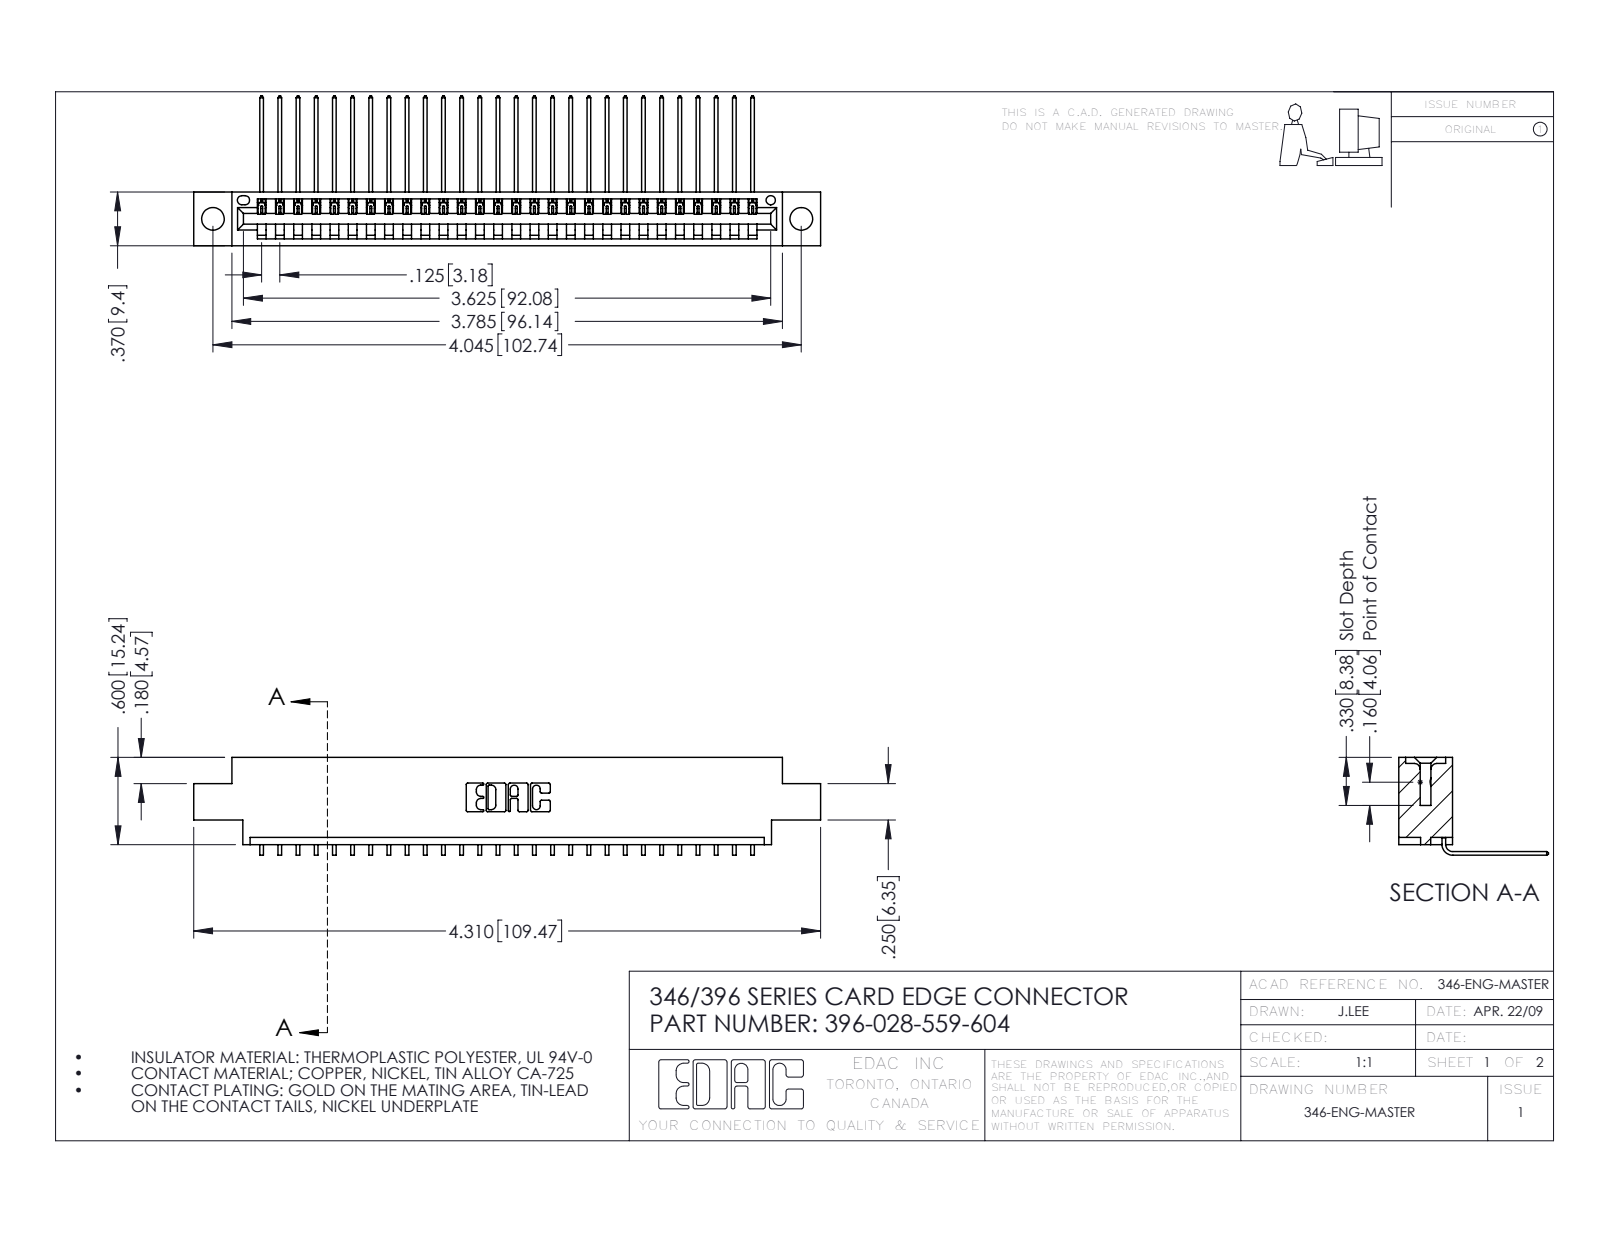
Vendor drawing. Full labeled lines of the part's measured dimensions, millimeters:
Part name (STEP PRODUCT): 346 Part_0.170 Offset - 0.156 Dia-TH; 345-292-001_558 559 Tail - 1; 396-028-559-604
STEP written by: SolidWorks 2016 (CONFIG_CONTROL_DESIGN)
Units: millimetres
Bodies: 29 solids, 1806 faces (1256 planar, 550 cylindrical, 0 other)
Overall size (bounding box): 109.5 × 26.2 × 17.1
Volume: 10 200 mm³ · Surface area: 13 160 mm²
Round holes (diameter × count): ⌀4 ×2, ⌀1.6 ×1
Partial cylindrical surfaces — rounded edges, fillets, slot ends (radius × count): R0.2 ×56, R0.3 ×22, R0.2 ×6, R0.8 ×6, R0.7 ×3, R0.8 ×2, R1 ×2, R0.4 ×1
Main face-to-face distances: 1.2, 8.2, 9.4, 6.4, 0.6, 1.8, 3.8, 5.6, 2.5, 4.4
Hole centre spacings: 6.2, 97.5, 102.7
